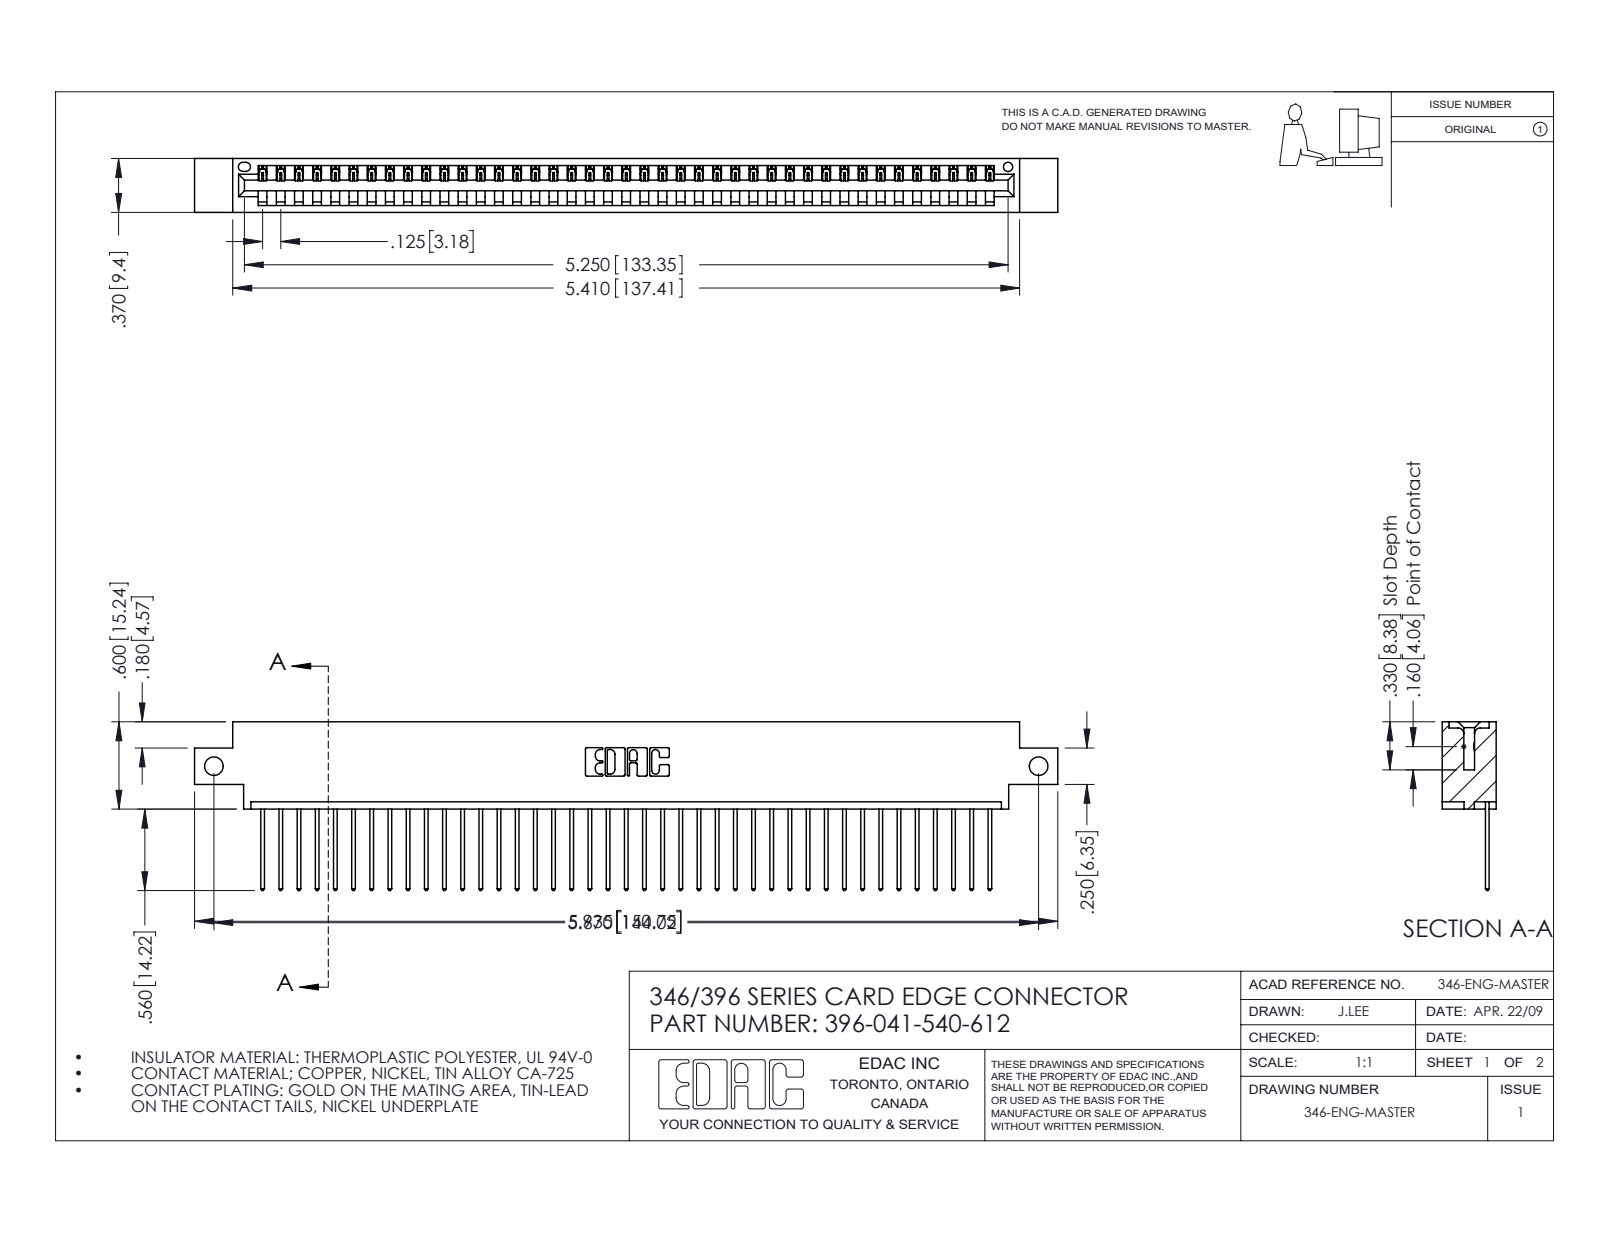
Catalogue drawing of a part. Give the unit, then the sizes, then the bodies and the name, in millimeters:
Units: millimetres
Overall size (bounding box): 150.7 × 29.5 × 9.4
Round holes (diameter × count): ⌀3.3 ×2, ⌀1.6 ×1
Partial cylindrical surfaces — rounded edges, fillets, slot ends (radius × count): R0.2 ×82, R0.3 ×82, R0.3 ×22, R0.2 ×6, R0.8 ×6, R0.7 ×3, R0.8 ×2, R1 ×2
Main face-to-face distances: 1.2, 8.2, 9.4, 6.4, 1.8, 7.6, 0.6, 3.8, 5.6, 2.5
Hole centre spacings: 144
Volume: 14 200 mm³ · Surface area: 18 210 mm²
Bodies: 42 solids, 2504 faces (1720 planar, 784 cylindrical, 0 other)
Part name (STEP PRODUCT): 396-041-540-612; 345-292-001_345-293-140; 346 Part_0.170 Offset - Side Mount
STEP written by: SolidWorks 2016 (CONFIG_CONTROL_DESIGN)
